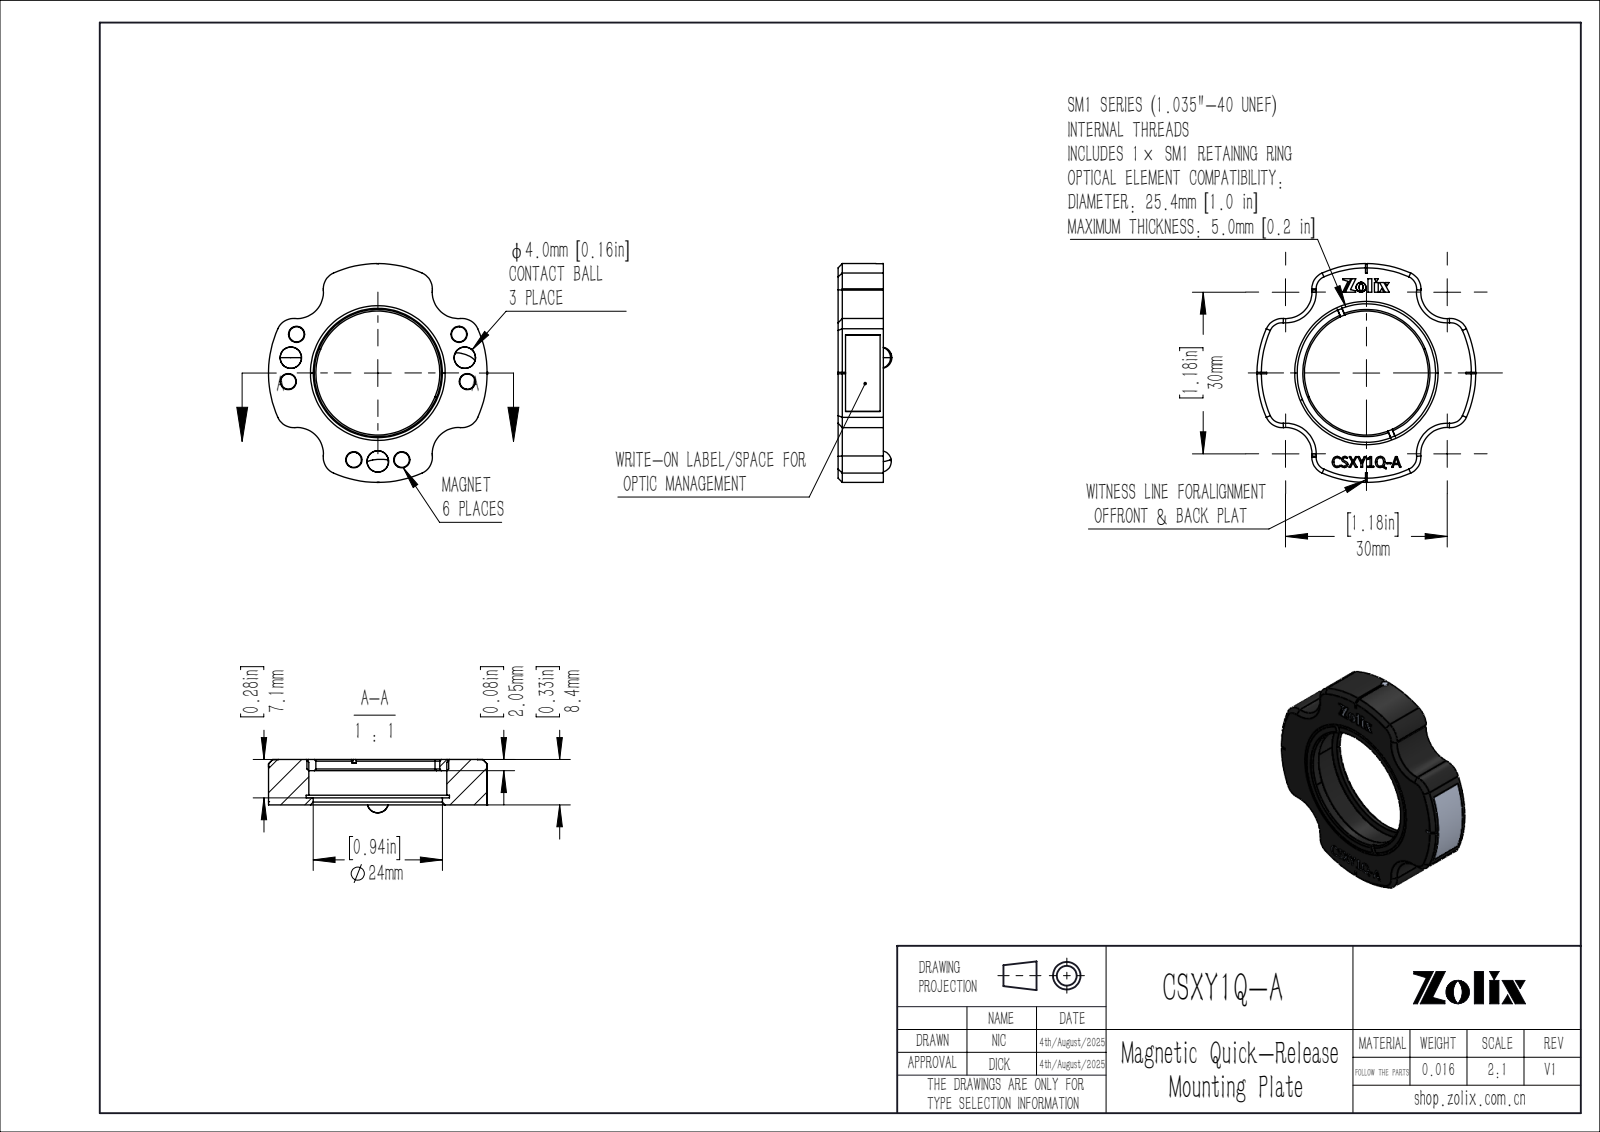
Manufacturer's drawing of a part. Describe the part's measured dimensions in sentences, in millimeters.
The part is named "CSXY1Q-A". Its 3-D file was written by "SolidWorks 2020 (CONFIG_CONTROL_DESIGN)". It is 11 solids with 493 faces: 281 planar, 70 cylindrical and 142 other. Overall it measures 40.6 by 40.6 by 9.98 millimeters. Its volume is 5 814 cubic millimeters and its surface area 4 392 square millimeters. Round holes: 6 of diameter 3, 3 of diameter 3.97, 1 of diameter 1.3, 1 of diameter 23, 1 of diameter 24, 1 of diameter 25.6, 1 of diameter 26.6. Round bosses or shafts: 1 of diameter 26.29. Partial cylindrical surfaces (rounded edges, fillets, slot ends): 8 of radius 3.2, 4 of radius 4.9, 1 of radius 20.28, 1 of radius 20.3. The main face-to-face distances are 8.4, 1.3, 7.1, 6.35, 5.05, 2.05, 2.62, 1.32, 3.73, 5.78. The hole center spacings are 4.46, 16.7, 25.59, 8.91, 16.4, 18.94, 22.27, 25.13.
